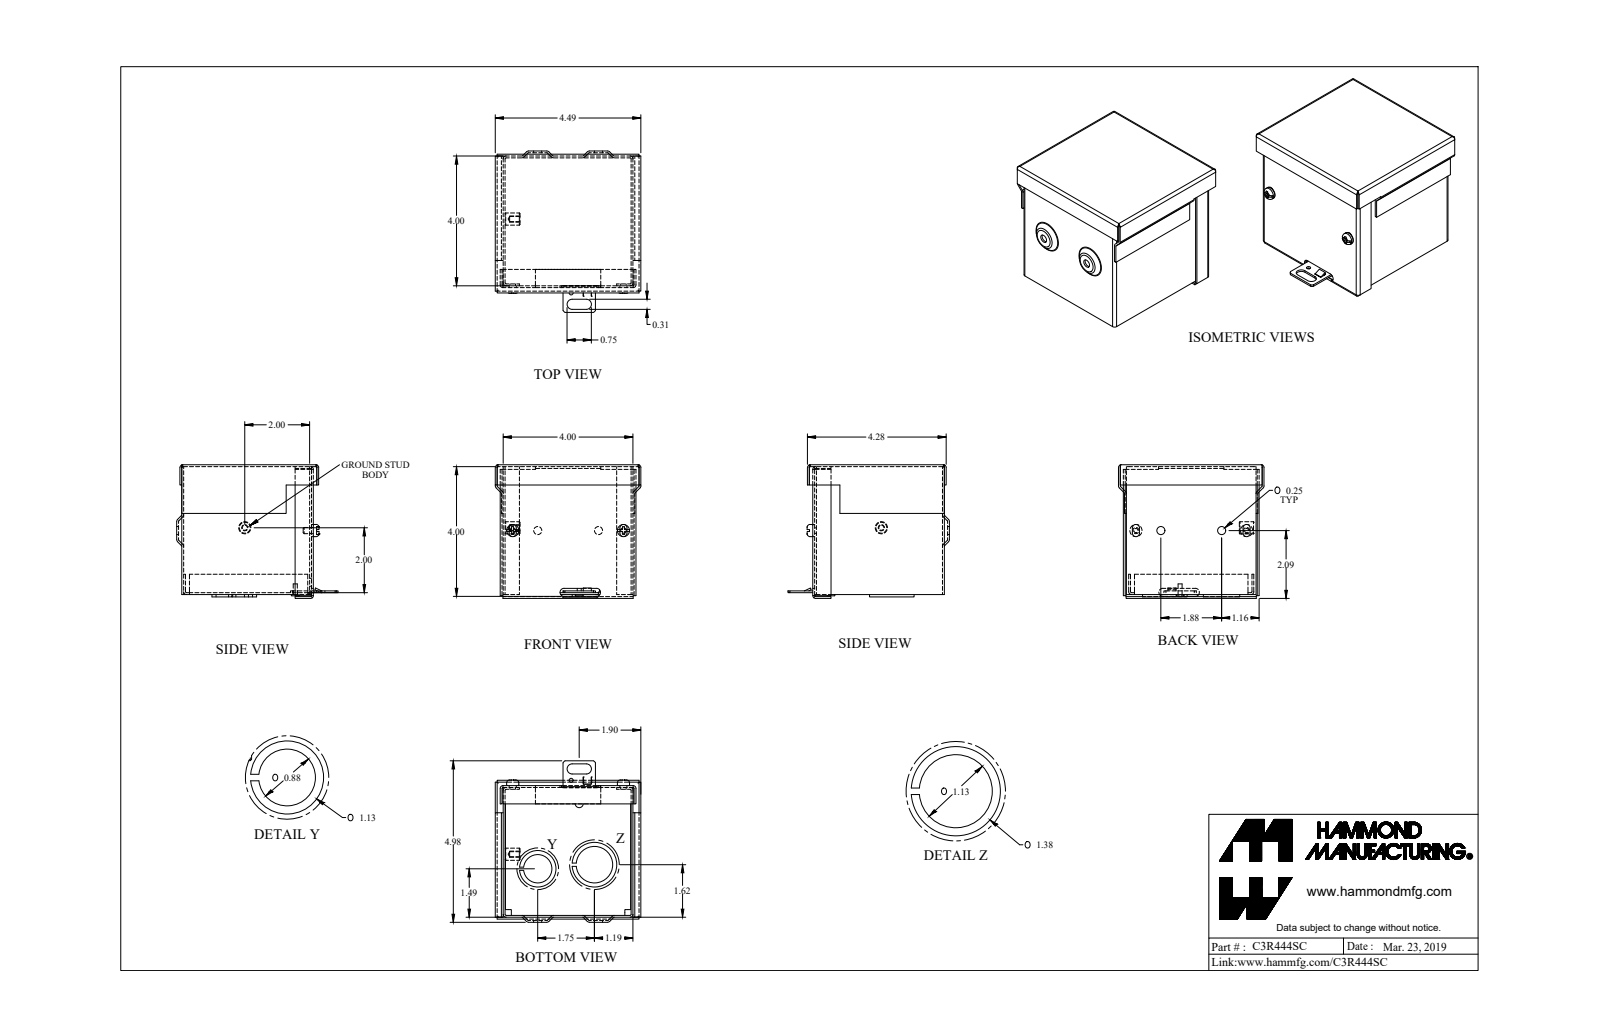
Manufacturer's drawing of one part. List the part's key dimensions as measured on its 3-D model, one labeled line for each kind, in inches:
Part name (STEP PRODUCT): C3R444SC
STEP written by: SolidWorks 2019 (AUTOMOTIVE_DESIGN)
Units: inches
Bodies: 9 solids, 277 faces (175 planar, 76 cylindrical, 26 other)
Overall size (bounding box): 4.977 × 4.489 × 4.12
Volume: 7.712 in³ · Surface area: 270.9 in²
Round holes (diameter × count): ⌀0.17 ×2, ⌀0.25 ×2, ⌀0.125 ×1, ⌀0.137 ×1, ⌀0.156 ×1, ⌀0.875 ×1, ⌀1.125 ×1
Round bosses / shafts (diameter × count): ⌀0.375 ×2, ⌀0.19 ×2, ⌀1.375 ×1, ⌀1.125 ×1, ⌀0.375 ×1, ⌀0.125 ×1
Partial cylindrical surfaces — rounded edges, fillets, slot ends (radius × count): R0.029 ×21, R0.086 ×21, R0.125 ×8, R0.109 ×4, R0.156 ×2
Main face-to-face distances: 0.057, 4, 3.943, 0.057, 3.886, 4.057, 3.886, 3.943, 0.114, 0.244
Hole centre spacings: 0.77, 2.644, 0.763, 1.754, 1.875, 1.938, 2.38, 2.699
